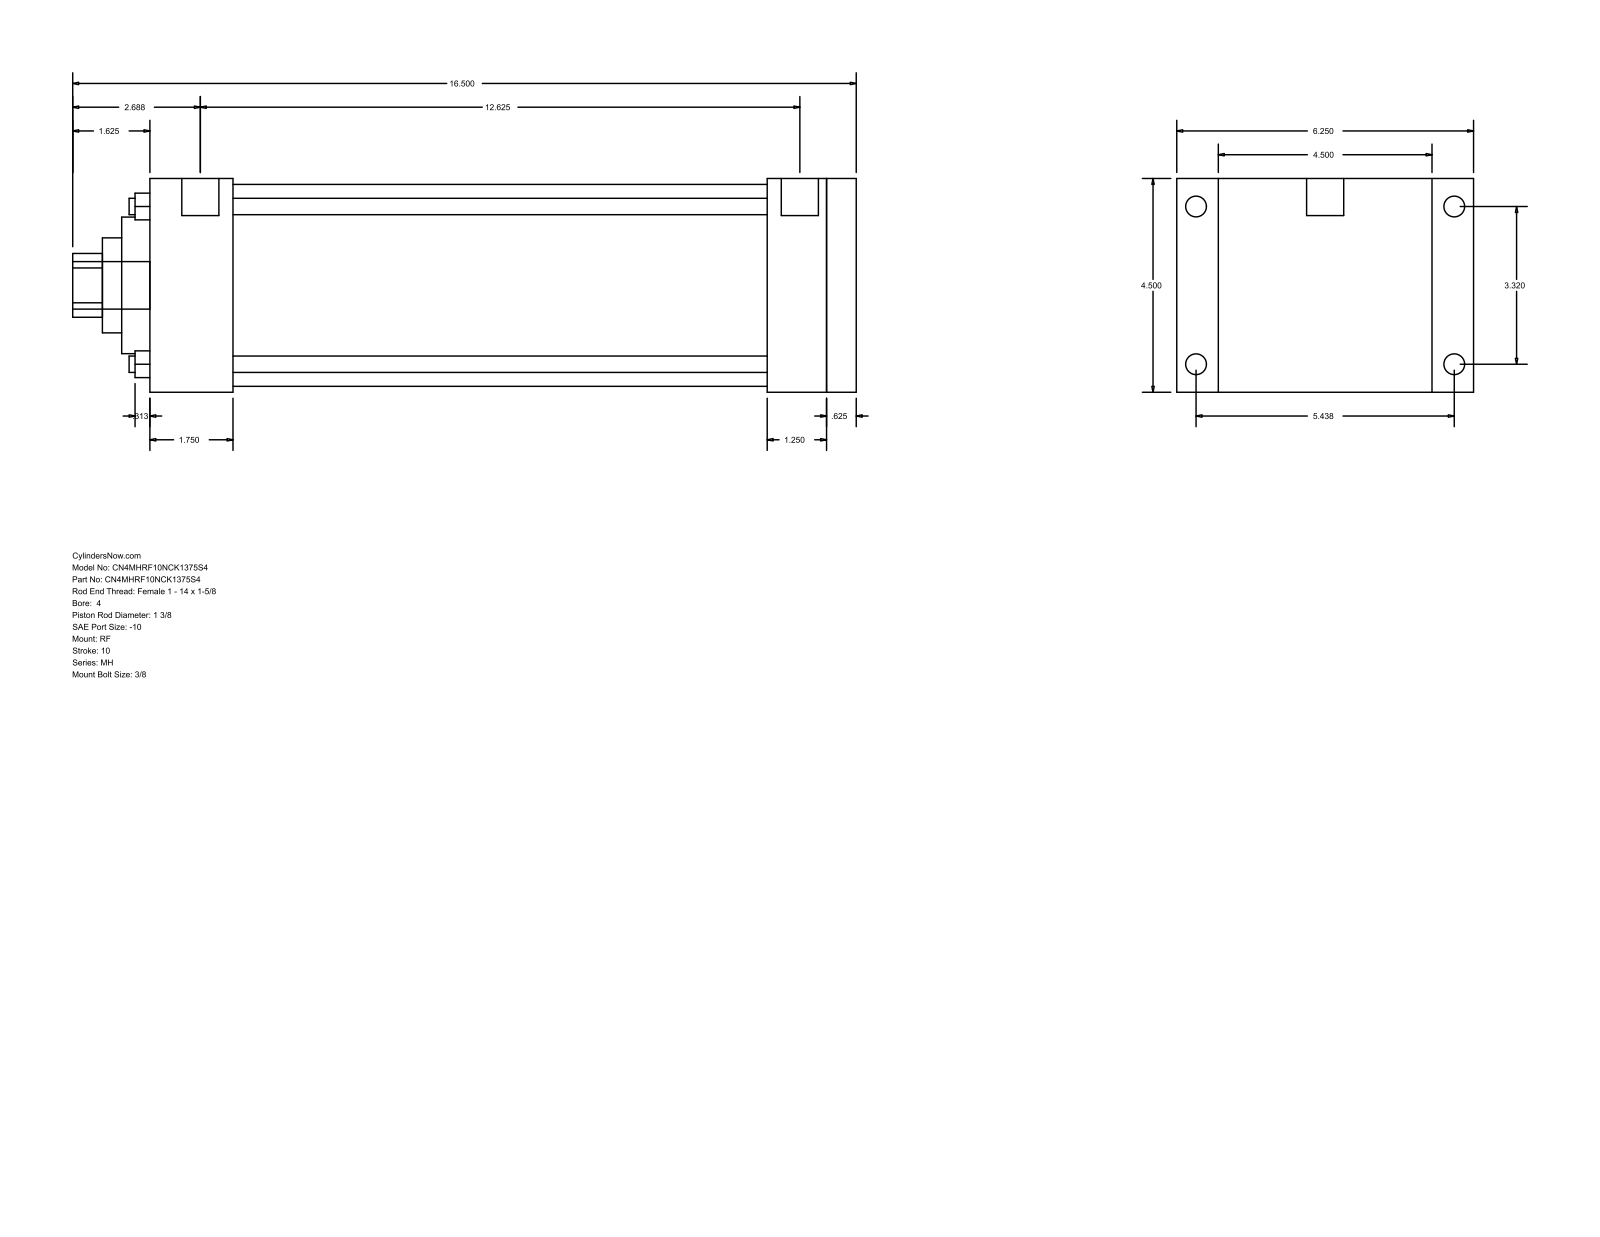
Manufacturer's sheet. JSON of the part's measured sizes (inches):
{"part_name": "MH_RF__0400_1.375", "step_written_by": "GSSL Pune (CONFIG_CONTROL_DESIGN)", "units": "inches", "bodies": {"solids": 0, "faces": 94, "planar": 65, "cylindrical": 29, "other": 0}, "overall_size": [16.5, 6.25, 4.5], "round_holes": [[0.345, 4], [1.375, 1], [2, 1], [2.875, 1], [4.25, 1]], "round_bosses_or_shafts": [[0.438, 4], [0.344, 4], [0.781, 2], [1, 1]], "partial_cylinders_radius": [[0.672, 1]], "face_to_face_distances": [4.5, 14.875, 14.25, 0.625, 1.75, 12.5, 13.125, 13, 11.25, 1.25], "hole_center_spacings": [2.347, 3.32, 4.695]}
